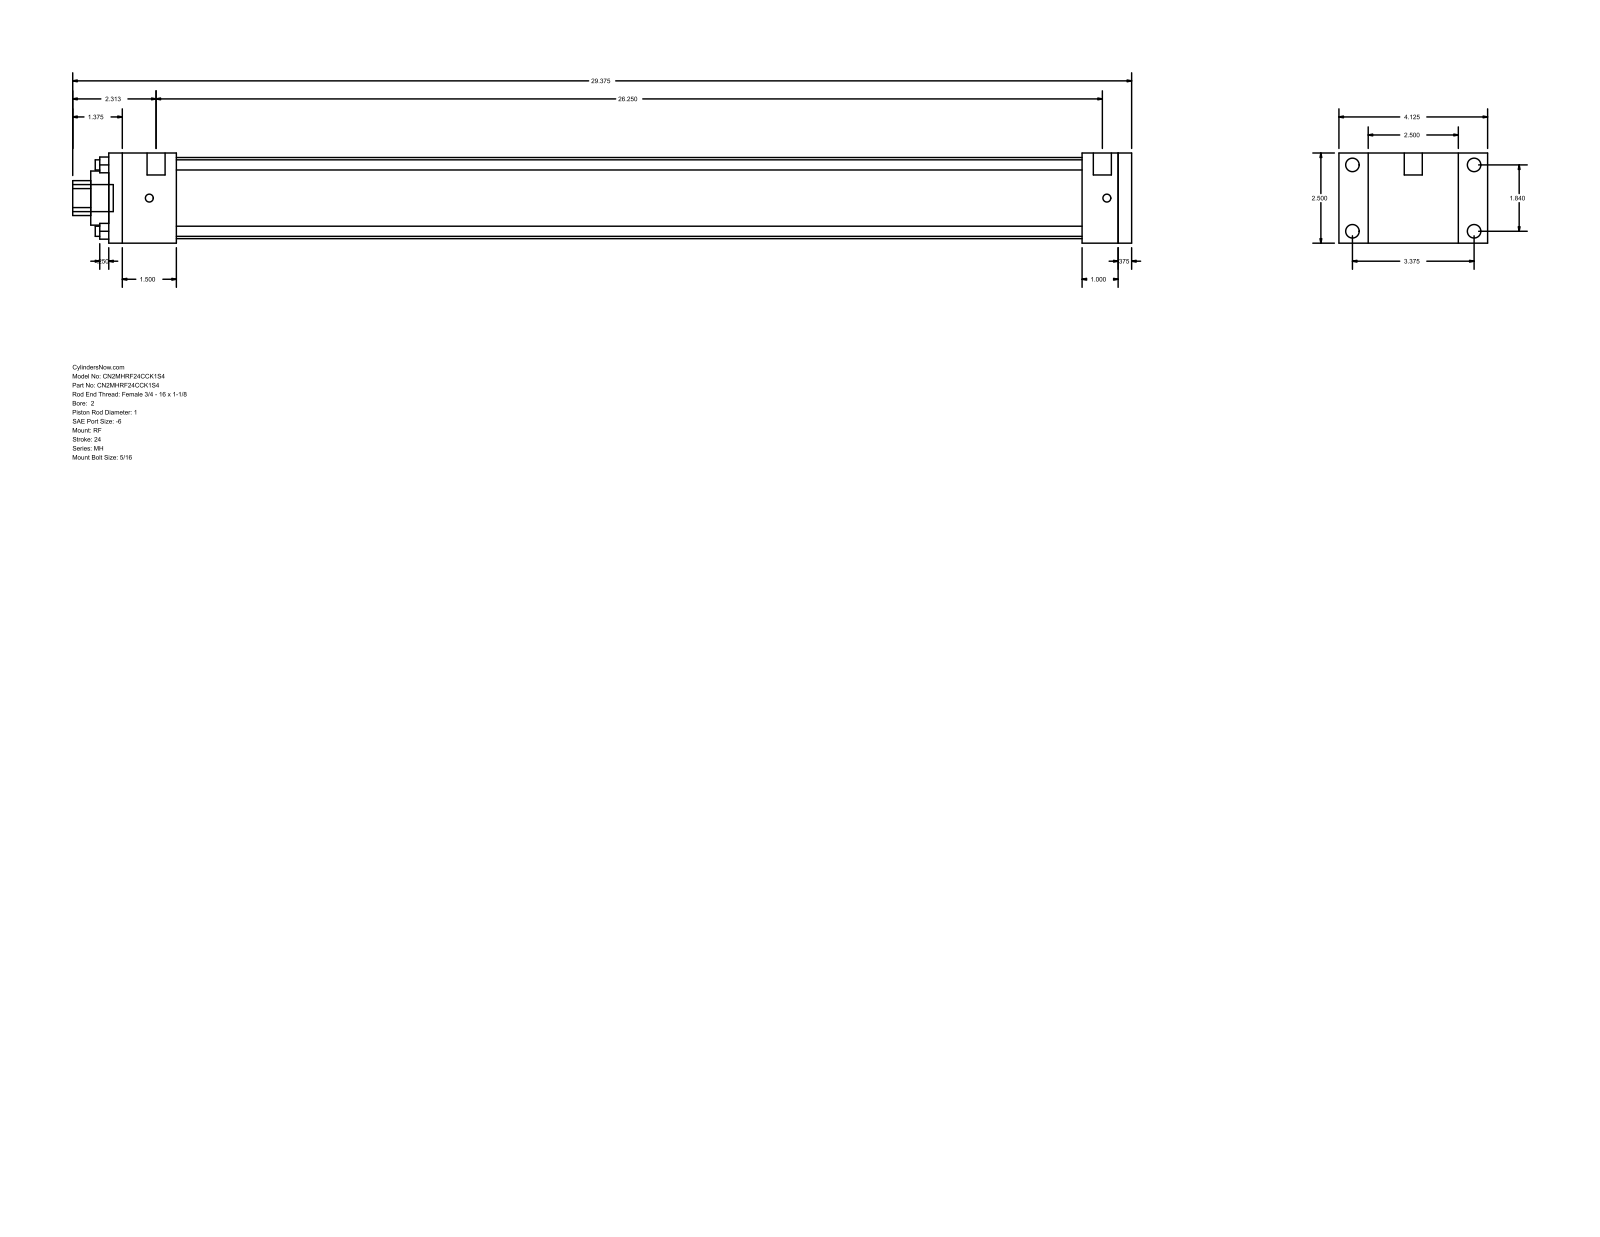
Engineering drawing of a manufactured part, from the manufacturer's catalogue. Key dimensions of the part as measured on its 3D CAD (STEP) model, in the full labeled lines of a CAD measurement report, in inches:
Part name (STEP PRODUCT): MH_RF__0200_1
STEP written by: GSSL Pune (CONFIG_CONTROL_DESIGN)
Units: inches
Bodies: 0 solids, 92 faces (64 planar, 28 cylindrical, 0 other)
Overall size (bounding box): 29.375 × 4.125 × 2.5
Round holes (diameter × count): ⌀0.281 ×4, ⌀1 ×1, ⌀1.5 ×1, ⌀2.25 ×1
Round bosses / shafts (diameter × count): ⌀0.375 ×4, ⌀0.219 ×4, ⌀0.5 ×2, ⌀0.75 ×1
Partial cylindrical surfaces — rounded edges, fillets, slot ends (radius × count): R0.484 ×1
Main face-to-face distances: 2.5, 0.375, 28.375, 28, 0.813, 1, 1.875, 27, 25.125, 26.125
Hole centre spacings: 1.301, 1.84, 2.602
